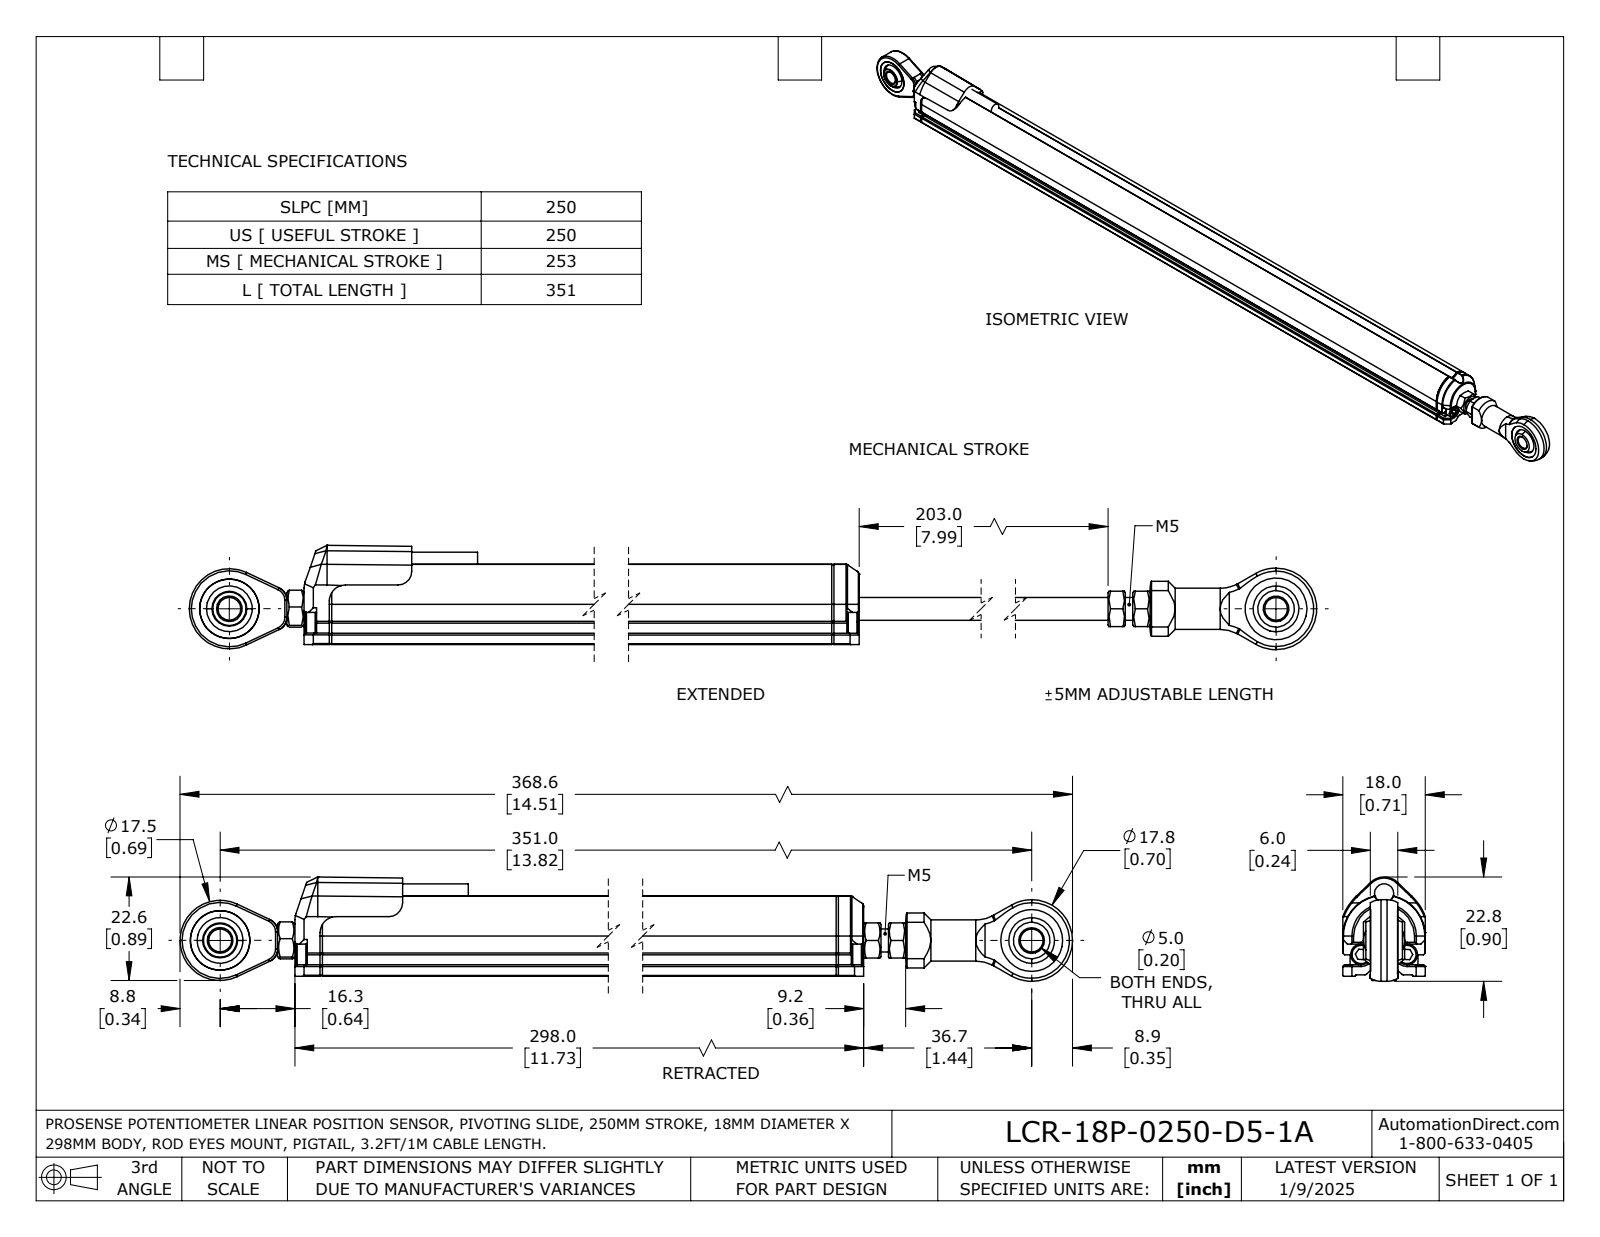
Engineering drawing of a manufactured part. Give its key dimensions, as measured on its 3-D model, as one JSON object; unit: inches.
{"part_name": "LCR-18P-0250-D5-1A", "step_written_by": "SolidWorks 2023 (AUTOMOTIVE_DESIGN)", "units": "inches", "bodies": {"solids": 20, "faces": 515, "planar": 289, "cylindrical": 136, "other": 90}, "overall_size": [14.514, 0.896, 0.709], "volume_in3": 5.139, "surface_area_in2": 50.85, "round_holes": [[0.197, 4], [0.102, 2], [0.104, 2], [0.394, 2], [0.213, 1], [0.272, 1], [0.512, 1], [0.531, 1]], "round_bosses_or_shafts": [[0.181, 4], [0.113, 3], [0.059, 2], [0.354, 1], [0.165, 1], [0.113, 1]], "partial_cylinders_radius": [[0.008, 12], [0.004, 10], [0.02, 8], [0.012, 6], [0.018, 6], [0.016, 4], [0.039, 4], [0.043, 4]], "face_to_face_distances": [0.709, 0.059, 0.063, 0.646, 0.071, 0.02, 11.28, 0.236, 0.087, 0.098], "hole_center_spacings": [0.231, 0.394, 0.23, 0.231, 13.819]}
